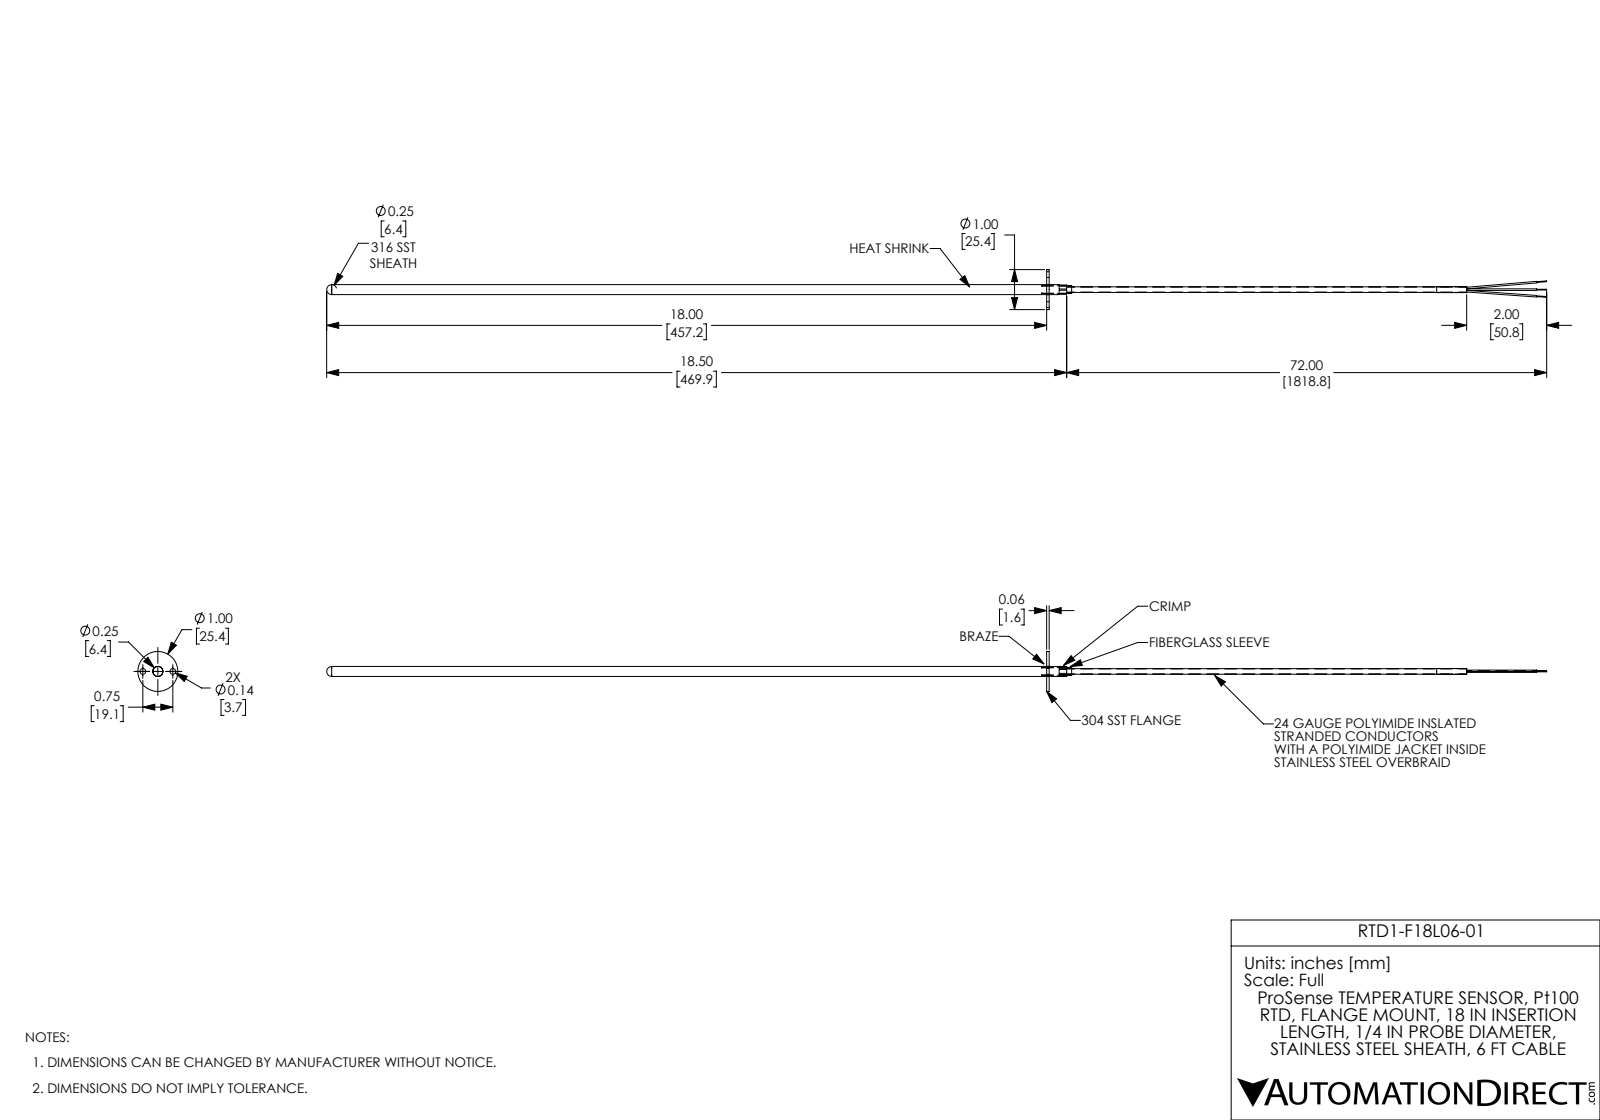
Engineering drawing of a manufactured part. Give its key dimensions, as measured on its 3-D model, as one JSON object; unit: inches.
{"part_name": "RTD1-F18L06-01", "step_written_by": "SolidWorks 2017 (AUTOMOTIVE_DESIGN)", "units": "inches", "bodies": {"solids": 7, "faces": 70, "planar": 31, "cylindrical": 32, "other": 7}, "overall_size": [30.5, 1, 1], "volume_in3": 1.123, "surface_area_in2": 31.91, "round_holes": [[0.144, 3], [0.136, 1], [0.189, 1], [0.257, 1]], "round_bosses_or_shafts": [[1, 1], [0.25, 1], [0.19, 1], [0.188, 1], [0.148, 1], [0.14, 1], [0.132, 1], [0.04, 1]], "face_to_face_distances": [0.063, 0.5, 0.437, 0.231, 0.75, 0.125, 0.188, 0.625, 0.625, 0.562], "hole_center_spacings": [0.375, 0.375, 0.75]}
